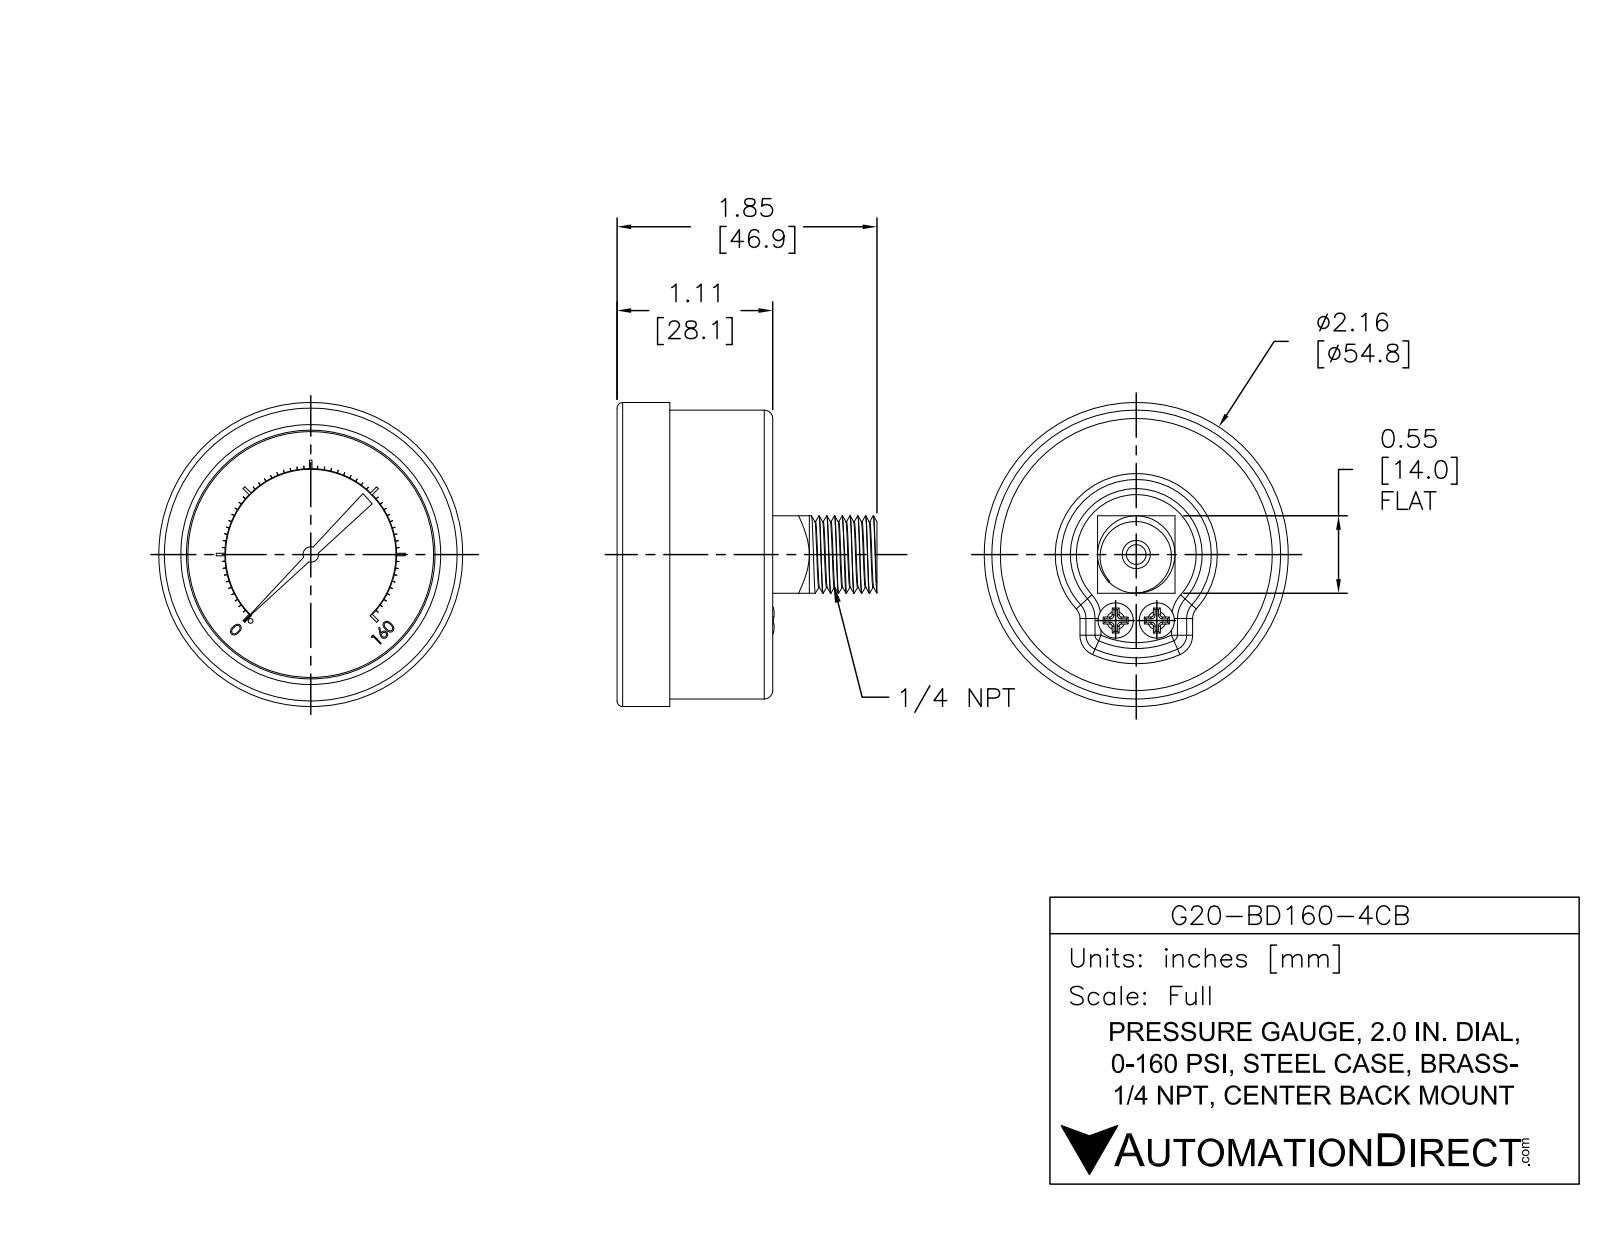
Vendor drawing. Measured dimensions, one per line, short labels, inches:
name: G20-BD160-4CB
written by: SolidWorks 2021 (AUTOMOTIVE_DESIGN)
unit: in
bodies: 1 solid, 377 faces (243 planar, 70 cylindrical, 64 other)
size: 2.158 × 2.158 × 1.845
volume: 3.201 in³; area: 18.16 in²
holes: 1× ⌀0.14, 1× ⌀1.745
bosses: 2× ⌀0.25, 1× ⌀2.158, 1× ⌀2.05, 1× ⌀0.55, 1× ⌀0.11, 1× ⌀0.102, 1× ⌀0.055
rounds: 4× R0.06, 1× R0.605, 1× R0.61
face distances: 0.815, 1.105, 0.29, 0.73, 0.085, 0.375, 0.1, 1.005, 0.715, 0.63
